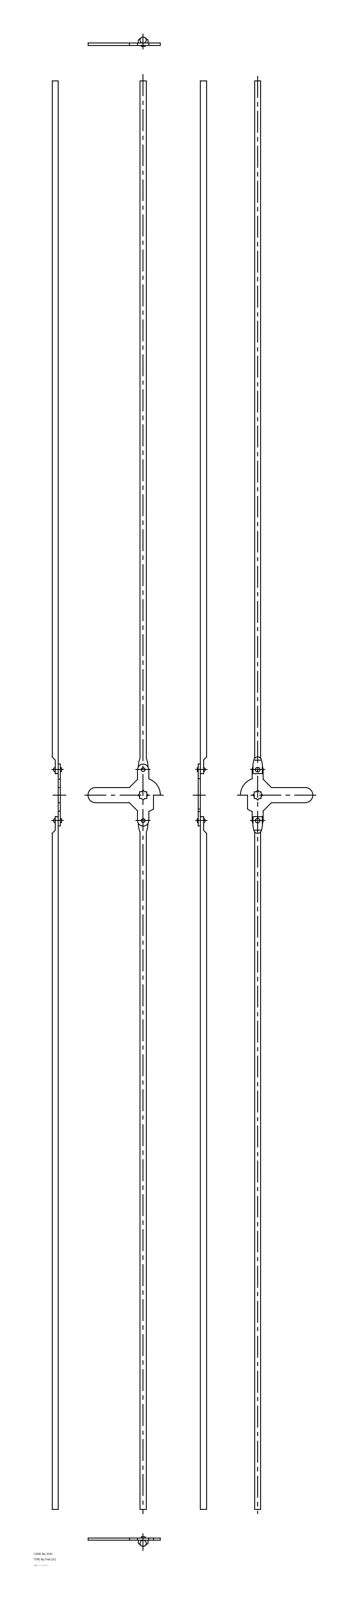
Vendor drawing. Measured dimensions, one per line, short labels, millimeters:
name: 67114483; 67114496; 67114509; 67114522 (+1 more)
written by: CADfix (AUTOMOTIVE_DESIGN)
unit: mm
bodies: 5 solids, 91 faces (0 planar, 0 cylindrical, 91 other)
size: 2074.01 × 105 × 13.7
volume: 138 793 mm³; area: 66 092 mm²
